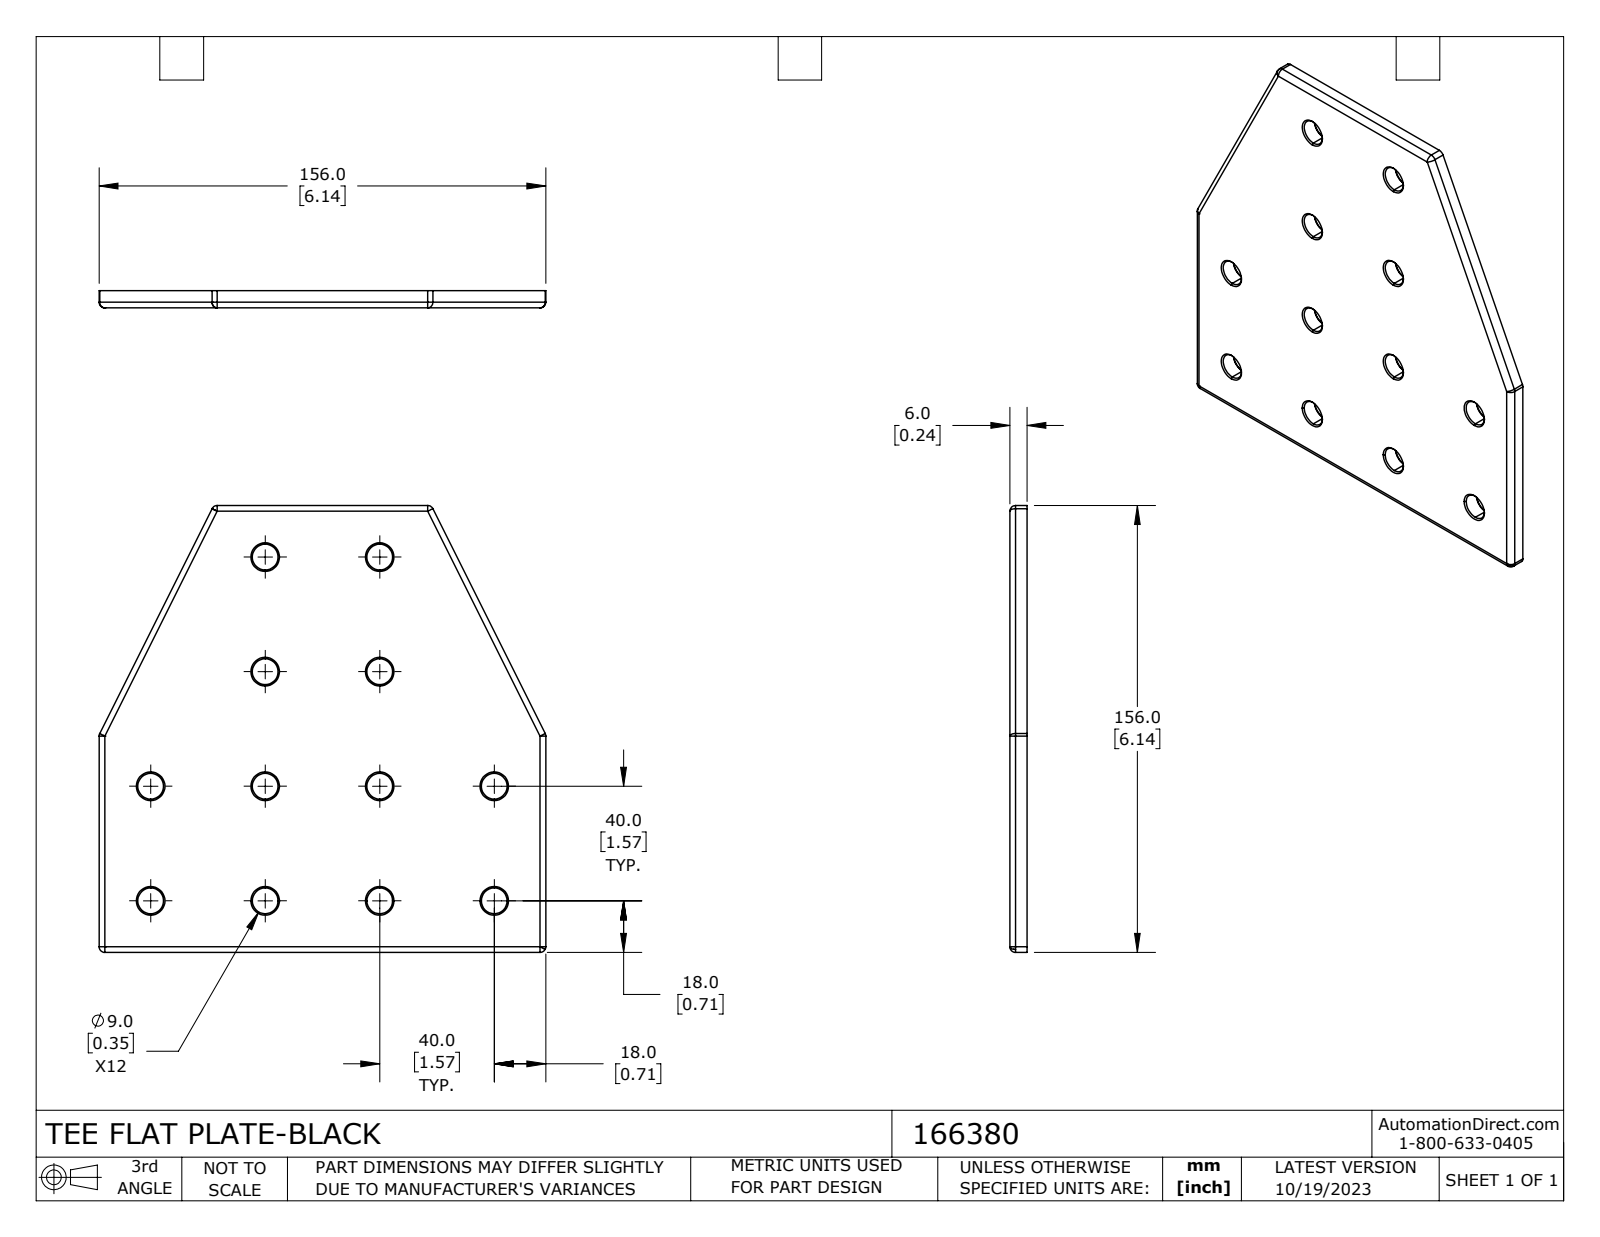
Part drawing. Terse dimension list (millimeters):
name: 166380
written by: SolidWorks 2023 (CONFIG_CONTROL_DESIGN)
unit: mm
bodies: 1 solid, 102 faces (8 planar, 36 cylindrical, 58 other)
size: 156 × 156 × 6
volume: 121 655 mm³; area: 45 466 mm²
holes: 12× ⌀9
rounds: 12× R2
face distances: 6, 156
hole spacings: 40, 89.44, 56.57, 80, 126.49, 113.14, 120, 144.22
